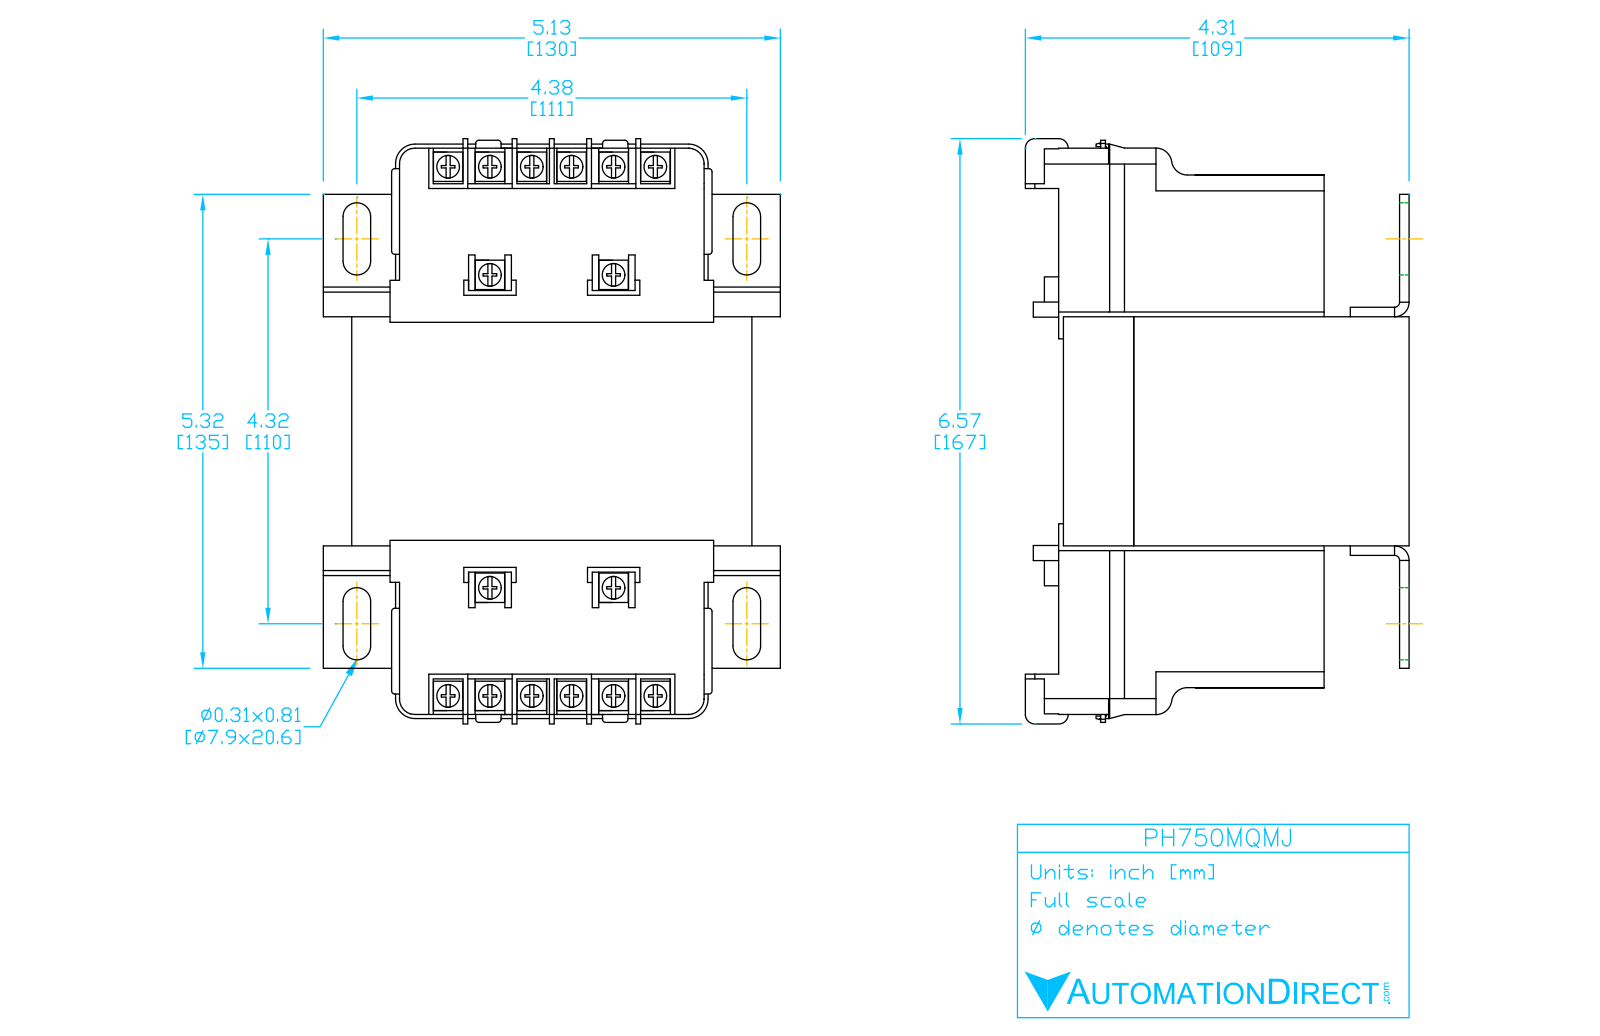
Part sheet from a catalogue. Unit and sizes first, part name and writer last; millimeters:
Units: millimetres
Overall size (bounding box): 166.9 × 130.2 × 107
Round holes (diameter × count): ⌀7 ×2
Partial cylindrical surfaces — rounded edges, fillets, slot ends (radius × count): R1 ×86, R5 ×18, R4 ×8, R2.5 ×4, R6.2 ×4, R1.6 ×2, R3.6 ×2
Main face-to-face distances: 78, 76, 80.7, 4.7, 16, 98, 95, 19, 14.2, 31
Hole centre spacings: 95
Volume: 1 437 000 mm³ · Surface area: 172 200 mm²
Bodies: 8 solids, 638 faces (370 planar, 190 cylindrical, 78 other)
Part name (STEP PRODUCT): PH750MQMJ
STEP written by: SolidWorks 2017 (AUTOMOTIVE_DESIGN)
